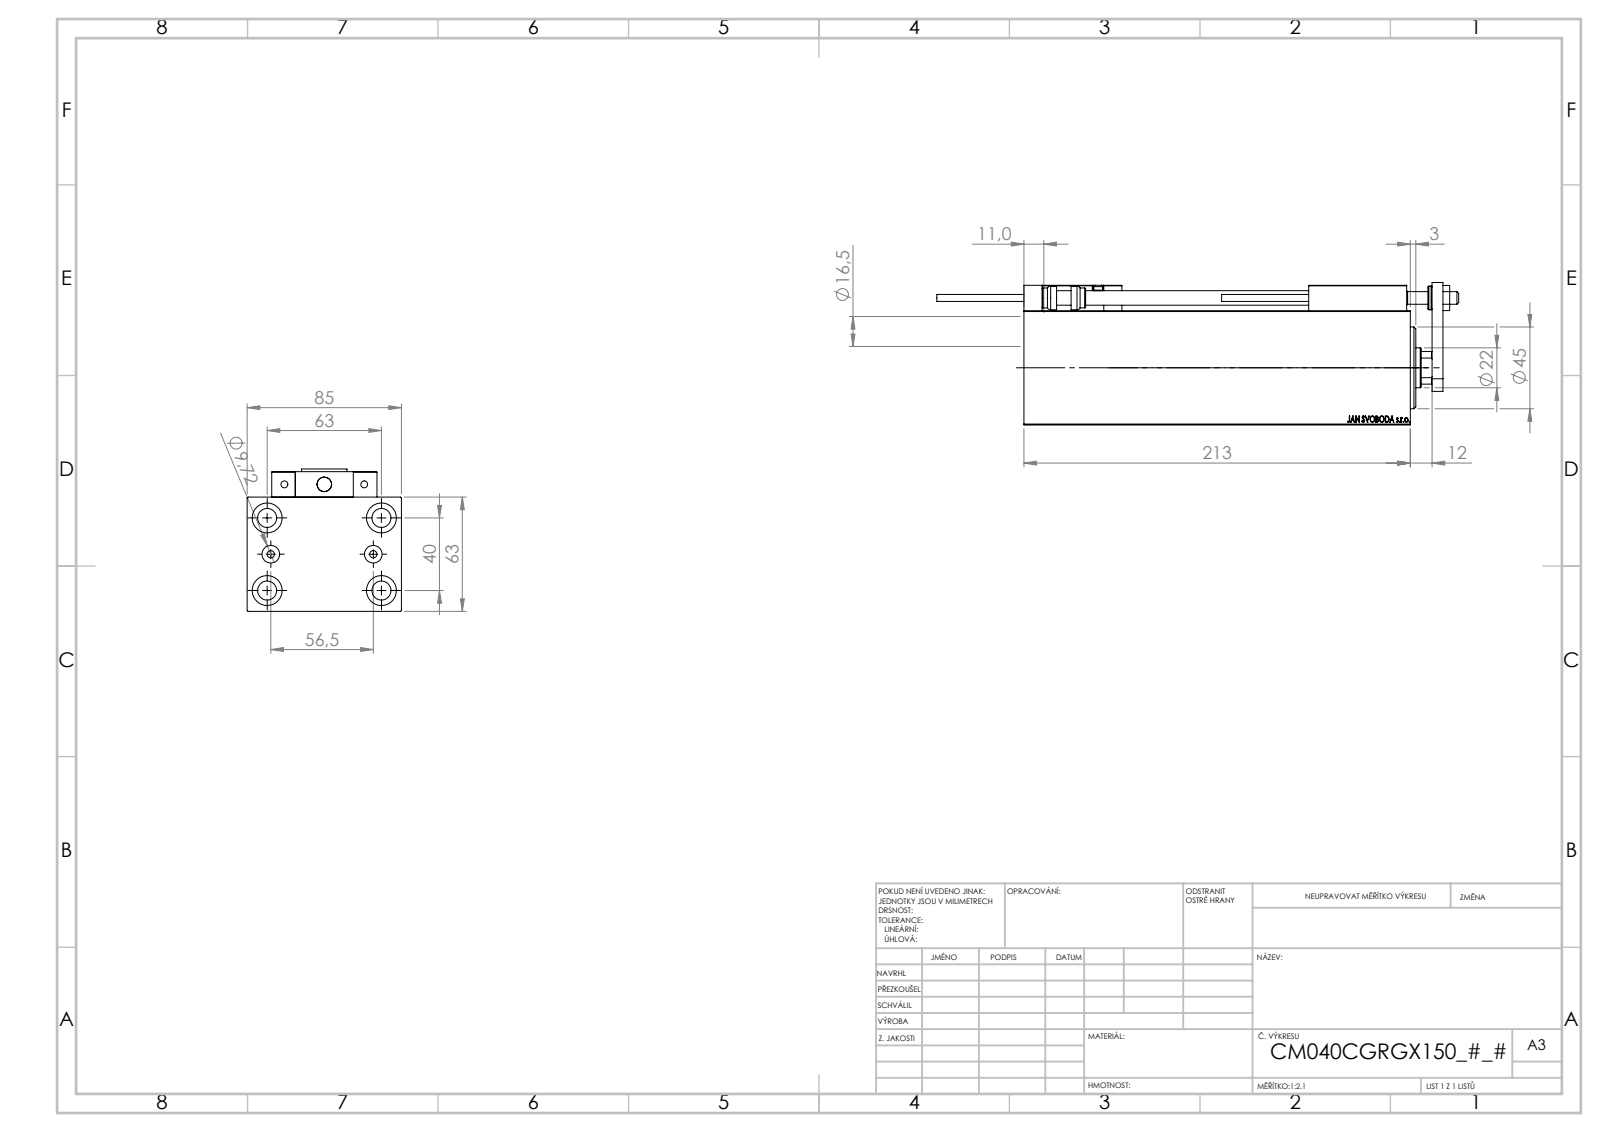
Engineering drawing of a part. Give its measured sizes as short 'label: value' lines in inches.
name: V450CM_VC_B; V450CM_C_VCP; MAGNET; ALLEN BOLT D5 (+7 more)
written by: SolidWorks 2019 (CONFIG_CONTROL_DESIGN)
unit: in
bodies: 23 solids, 1278 faces (560 planar, 184 cylindrical, 534 other)
size: 11.327 × 3.346 × 3.091
volume: 59.65 in³; area: 289.9 in²
holes: 6× ⌀0.157, 5× ⌀0.315, 5× ⌀0.65, 4× ⌀0.126, 4× ⌀0.413, 2× ⌀0.197, 2× ⌀0.383, 1× ⌀0.276, 1× ⌀0.492, 1× ⌀0.866, 1× ⌀1.004, 1× ⌀1.575
bosses: 2× ⌀0.197, 2× ⌀0.15, 1× ⌀0.512, 1× ⌀0.433
rounds: 30× R0.012, 2× R0.118, 1× R0.413
face distances: 2.48, 3.346, 0.472, 7.913, 8.386, 0.551, 3.031, 0.591, 0.709, 1.181
hole spacings: 1.469, 0.448, 0.787, 0.791, 0.807, 1.165, 1.169, 1.42
